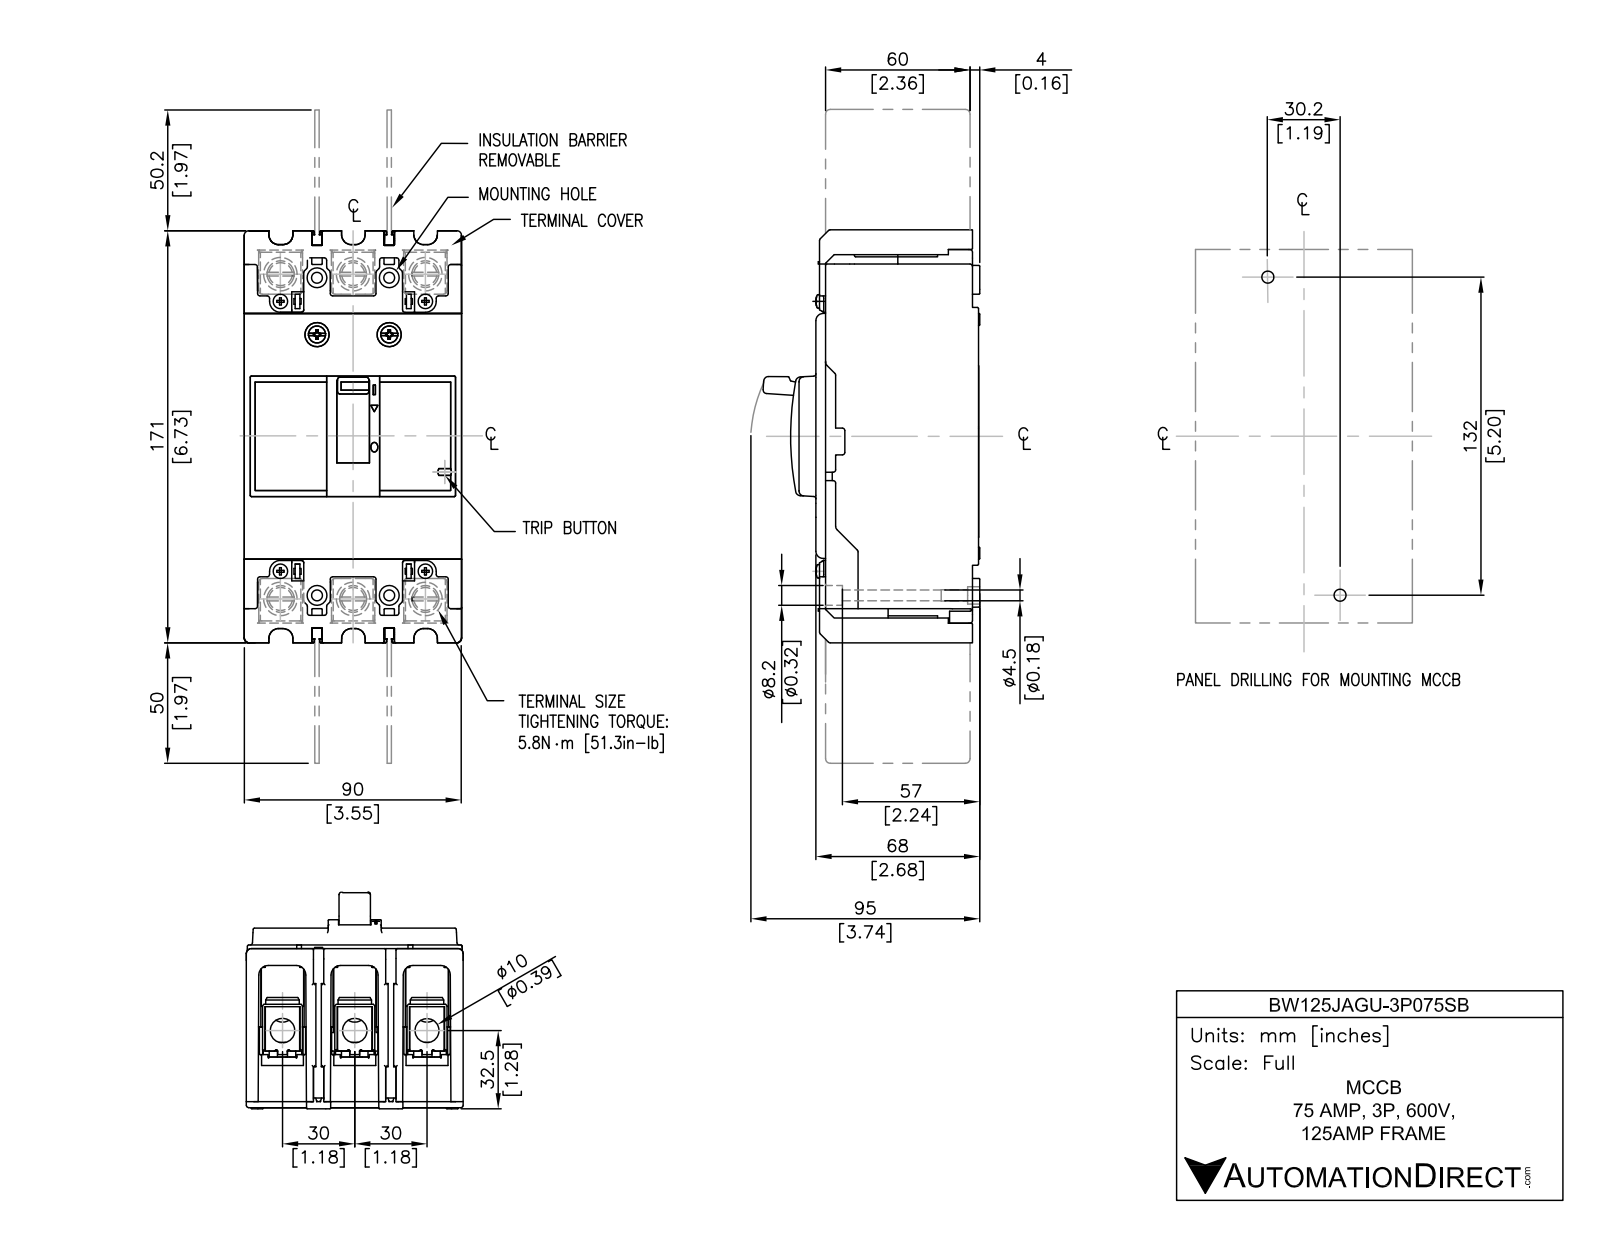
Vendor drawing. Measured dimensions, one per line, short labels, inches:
name: BW125JAGU-3P075SB
written by: SolidWorks 2018 (AUTOMOTIVE_DESIGN)
unit: in
bodies: 14 solids, 452 faces (340 planar, 88 cylindrical, 24 other)
size: 10.197 × 3.602 × 3.543
volume: 57.4 in³; area: 230.3 in²
holes: 6× ⌀0.315, 4× ⌀0.177, 4× ⌀0.323
bosses: 6× ⌀0.472
rounds: 12× R0.157, 6× R0.079, 6× R0.118
face distances: 1.181, 1.11, 1.252, 2.291, 2.433, 0.142, 3.543, 0.236, 2.402, 1.039
hole spacings: 0.593, 5.289, 1.181, 1.772, 5.444, 5.546, 5.315, 2.362
